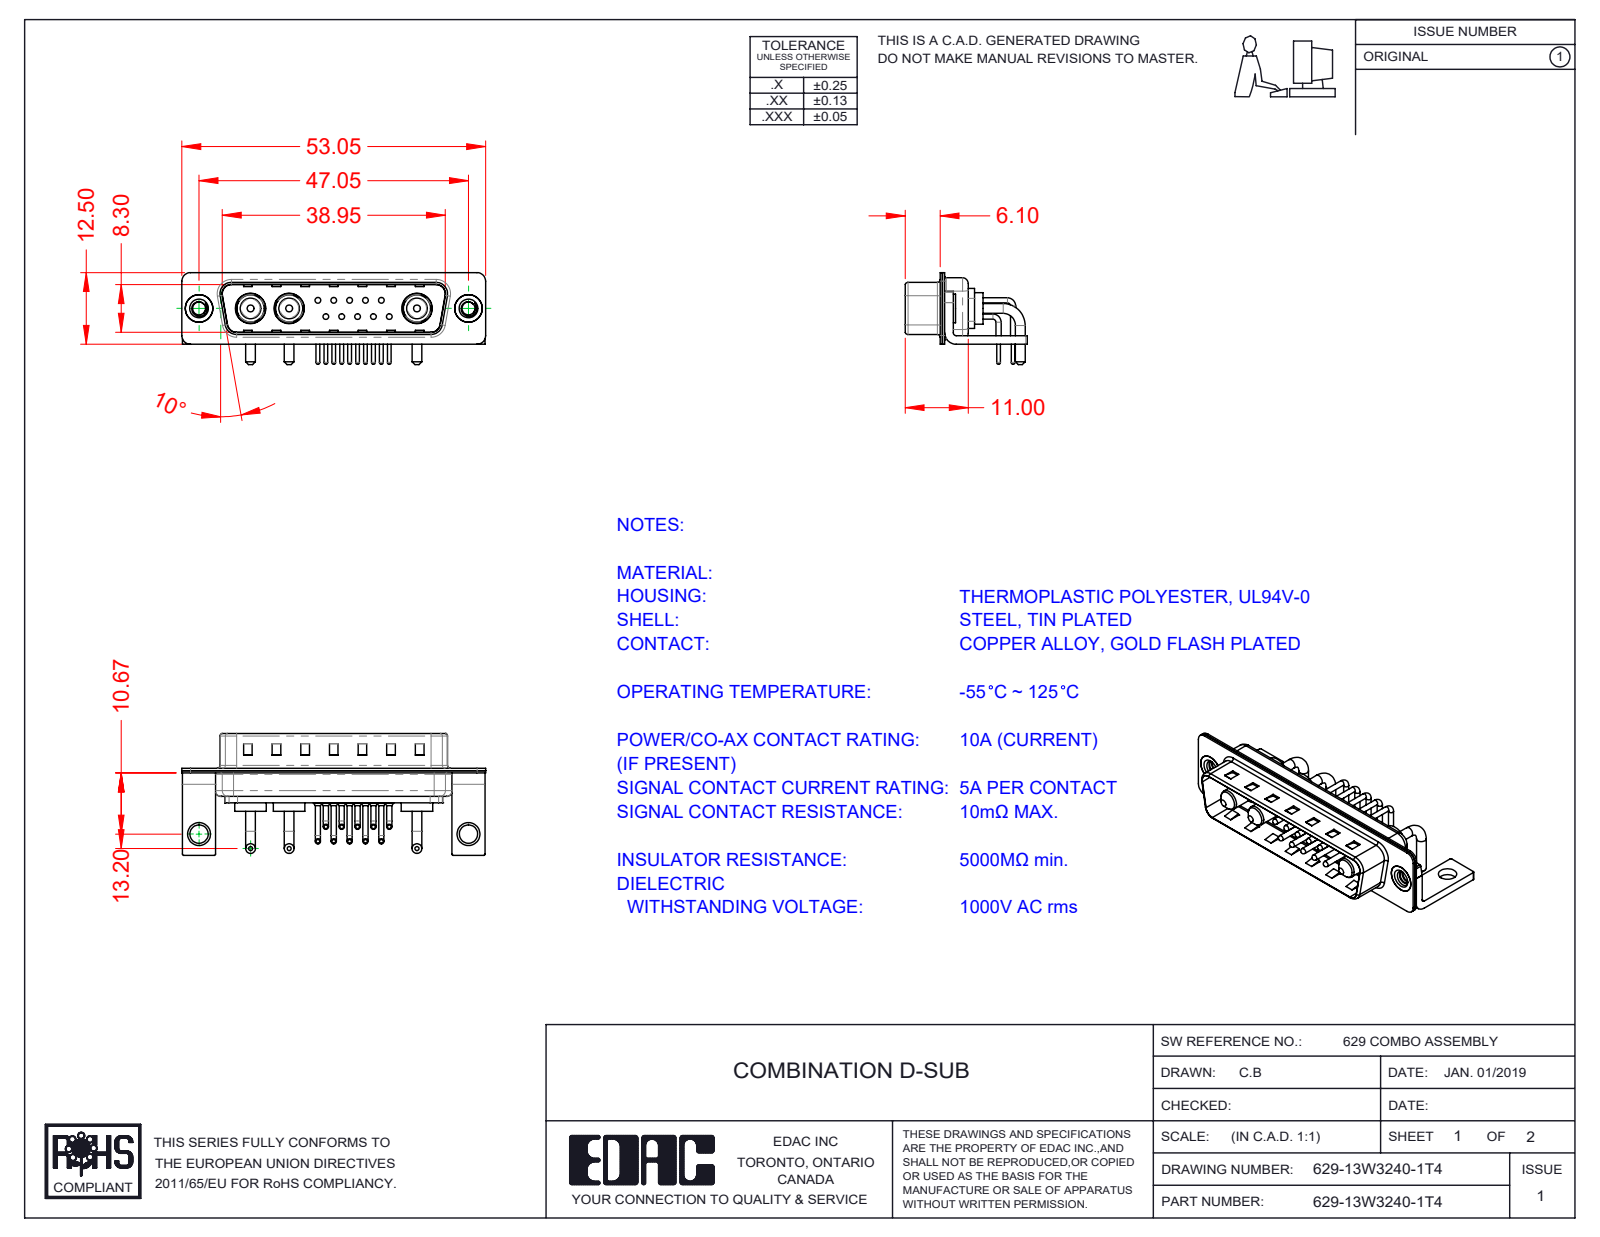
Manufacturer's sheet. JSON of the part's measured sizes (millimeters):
{"part_name": "629Combo Housing_13W3; Power Pin_10A RA; 629Combo Stabilizer Bracket; 629-13W3240-1T4 (+5 more)", "step_written_by": "SolidWorks 2020 (CONFIG_CONTROL_DESIGN)", "units": "millimeters", "bodies": {"solids": 23, "faces": 1645, "planar": 861, "cylindrical": 578, "other": 206}, "overall_size": [53.05, 21.3, 16.05], "volume_mm3": 3303, "surface_area_mm2": 7805, "round_holes": [[0.75, 10], [1.6, 10], [2, 10], [4.85, 3], [5.3, 3], [2.26, 2], [3.2, 2], [4, 2], [4.8, 2]], "round_bosses_or_shafts": [[0.9, 20], [1.5, 10], [1, 10], [0.65, 10], [1.7, 6], [5.5, 3], [5.2, 3], [4.75, 3]], "partial_cylinders_radius": [[0.25, 16], [1.5, 16], [2, 13], [1.01, 10], [0.5, 9], [1.6, 8], [0.6, 4], [0.65, 4]], "face_to_face_distances": [0.4, 0.8, 1.5, 9.5, 9.1, 8.7, 9.9, 5.2, 5.6, 0.6], "hole_center_spacings": [3.16, 2.77, 5.04, 5.54, 7.49, 5.03, 8.31, 10.11]}
